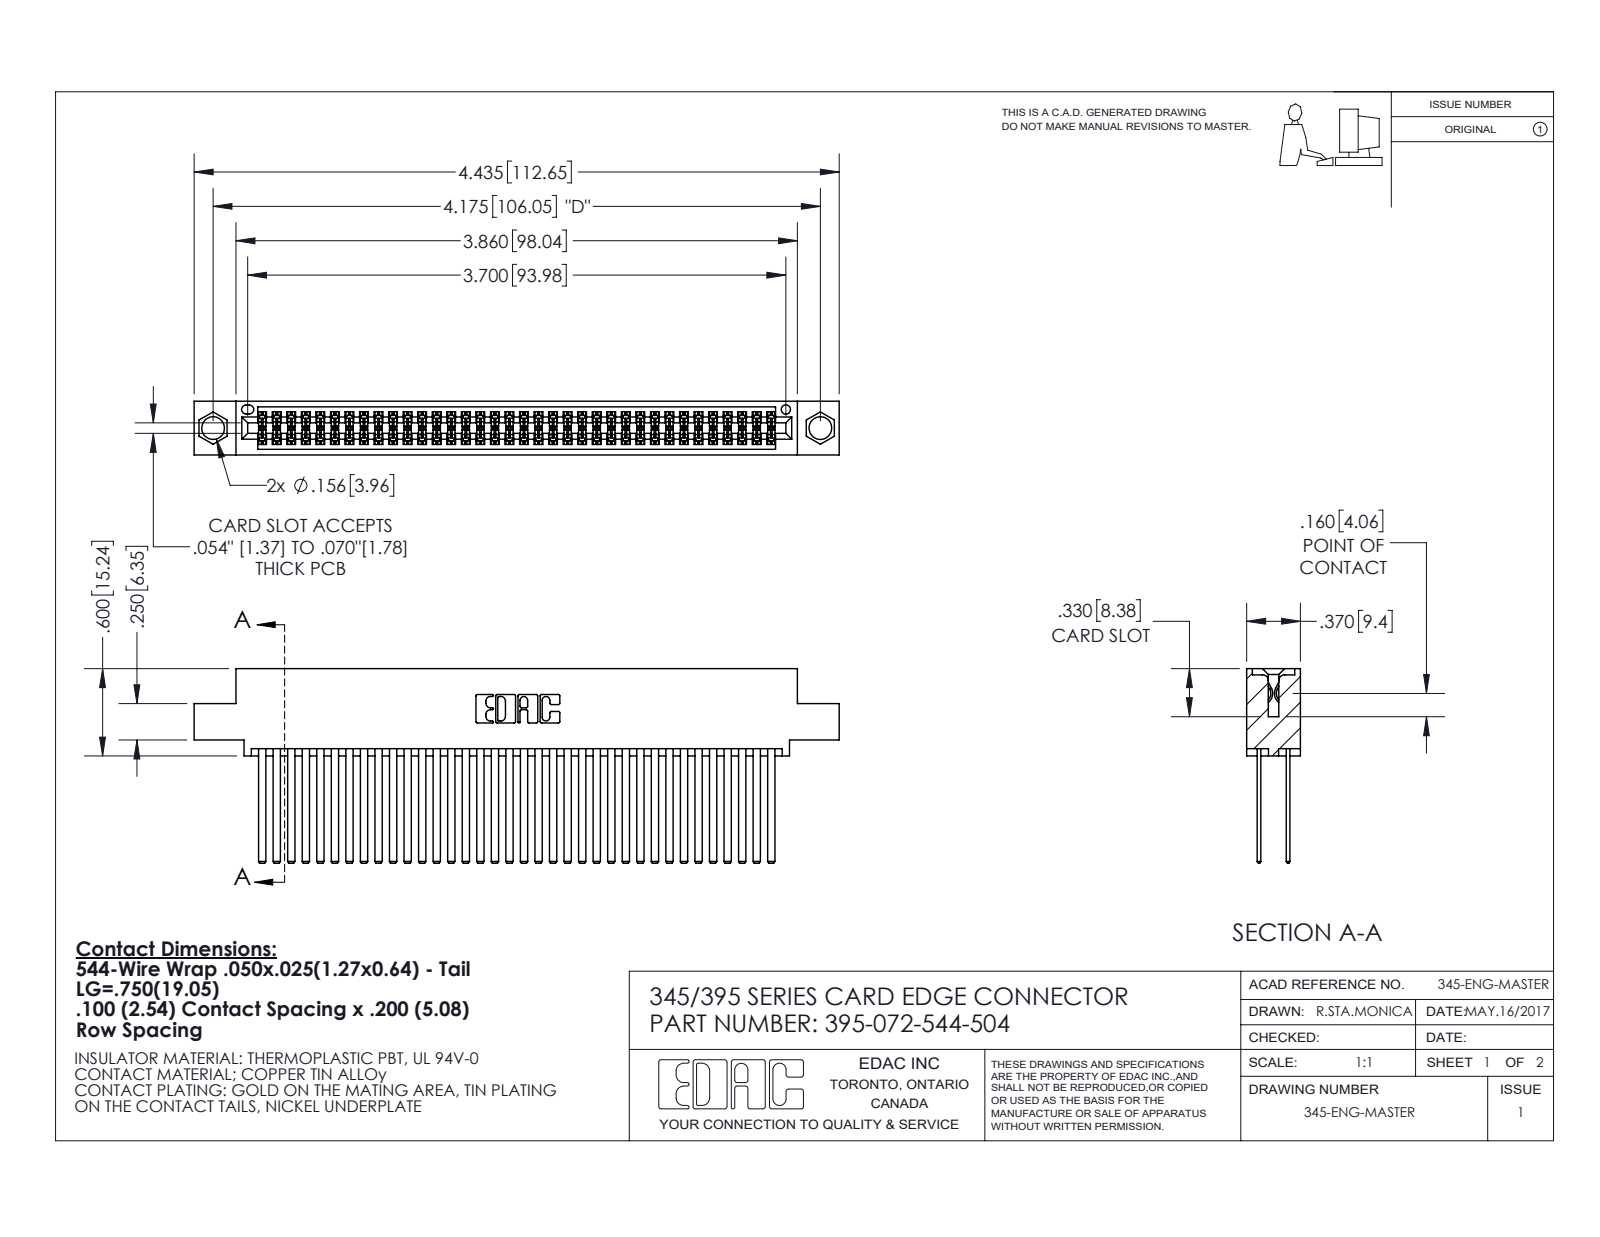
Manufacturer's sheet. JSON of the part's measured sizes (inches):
{"part_name": "345 Part_0.110 Offset - 0.156 Dia-TI; 345-292-001_345-293-144; 395-072-544-504", "step_written_by": "SolidWorks 2020 (CONFIG_CONTROL_DESIGN)", "units": "inches", "bodies": {"solids": 73, "faces": 3312, "planar": 2186, "cylindrical": 1126, "other": 0}, "overall_size": [4.435, 1.337, 0.37], "volume_in3": 0.715, "surface_area_in2": 31.16, "round_holes": [[0.156, 2], [0.064, 1]], "partial_cylinders_radius": [[0.006, 144], [0.01, 22], [0.007, 6], [0.031, 6], [0.026, 3], [0.014, 2], [0.019, 2], [0.022, 2]], "face_to_face_distances": [0.2, 0.025, 0.072, 0.098, 0.272, 0.298, 0.225, 0.175, 0.37, 0.05], "hole_center_spacings": [0.27, 3.939, 4.175]}
